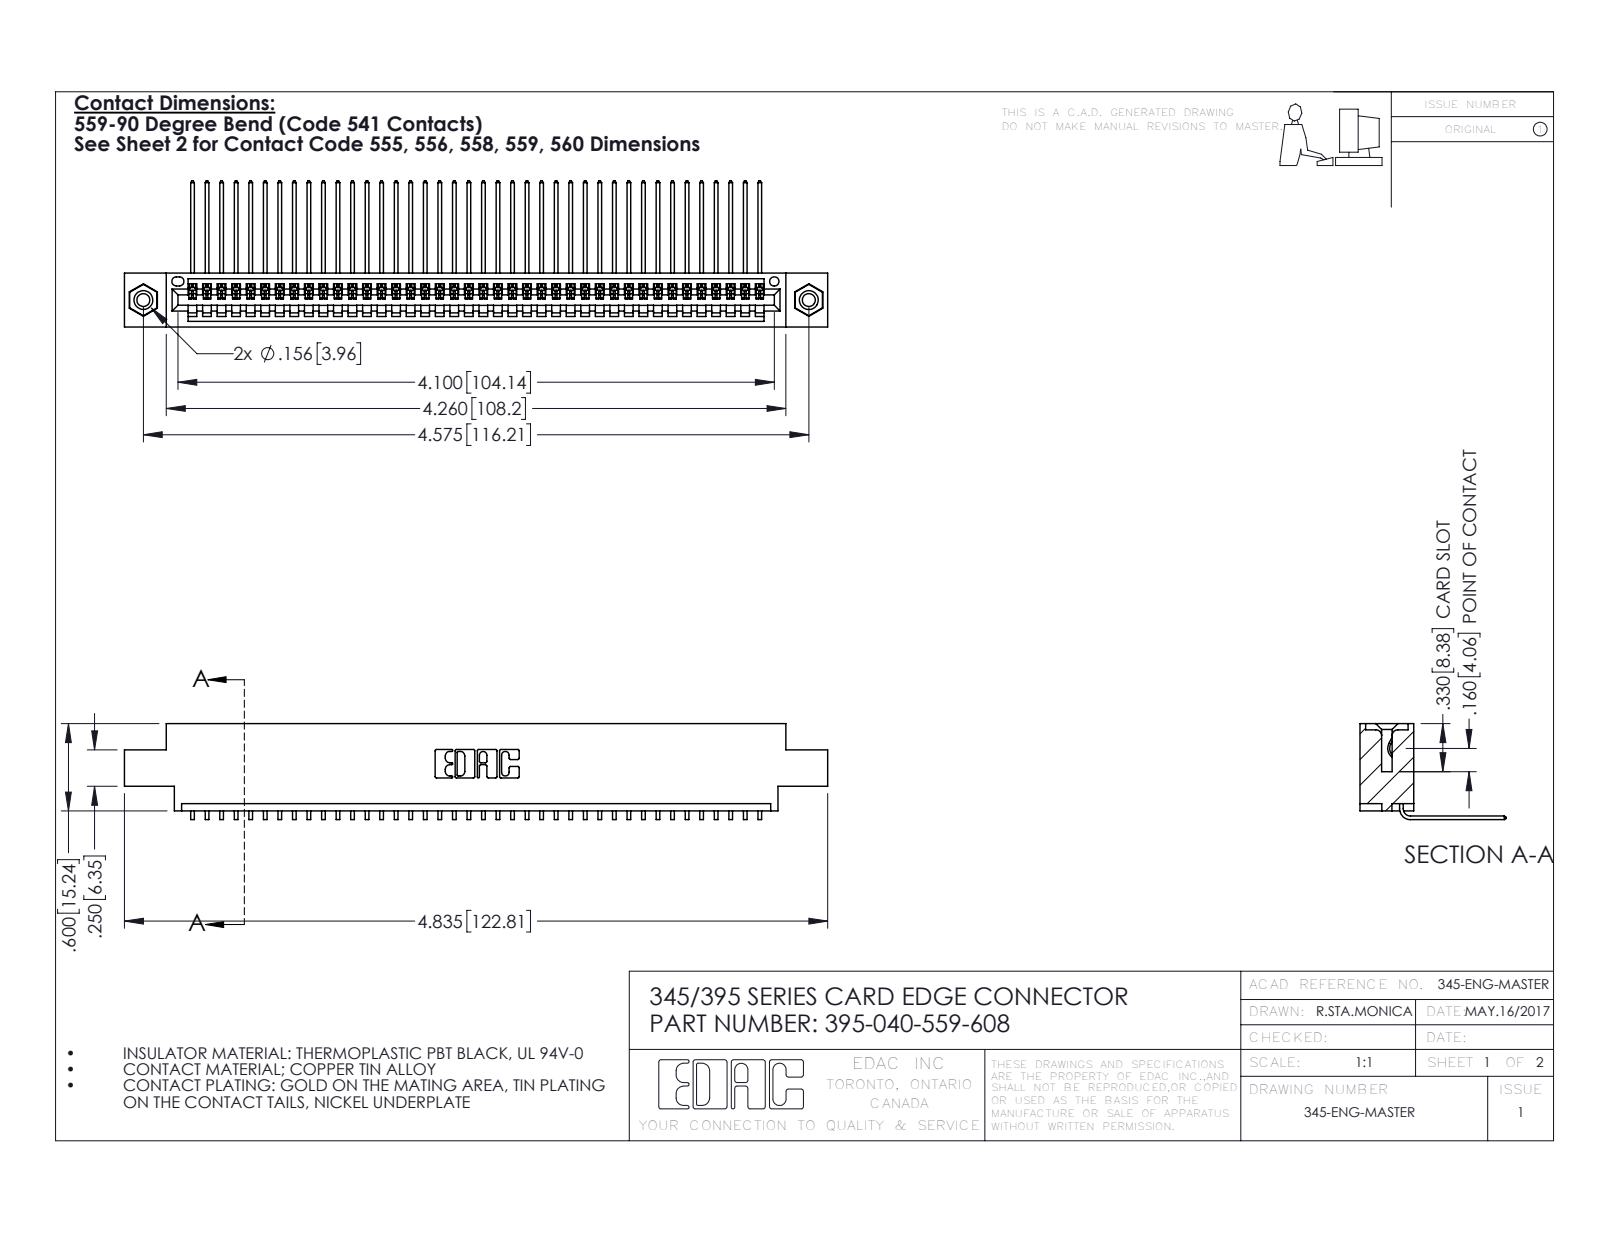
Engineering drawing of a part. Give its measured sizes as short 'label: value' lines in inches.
name: 395-040-559-608; 345-292-001_558 559 Tail - 1; 345 Part_0.170 Offset - 0.156 Dia-TI; 345-250-001_345-250-003-102
written by: SolidWorks 2016 (CONFIG_CONTROL_DESIGN)
unit: in
bodies: 43 solids, 2590 faces (1796 planar, 778 cylindrical, 16 other)
size: 4.835 × 1.005 × 0.659
volume: 0.712 in³; area: 25.42 in²
holes: 2× ⌀0.089, 2× ⌀0.125, 2× ⌀0.156, 1× ⌀0.064
bosses: 2× ⌀0.155
rounds: 80× R0.006, 22× R0.01, 6× R0.007, 6× R0.031, 3× R0.026, 2× R0.031, 2× R0.04, 1× R0.014
face distances: 0.072, 0.298, 0.37, 0.2, 0.098, 0.272, 0.025, 0.225, 0.175, 0.149
hole spacings: 0.27, 4.339, 4.575
